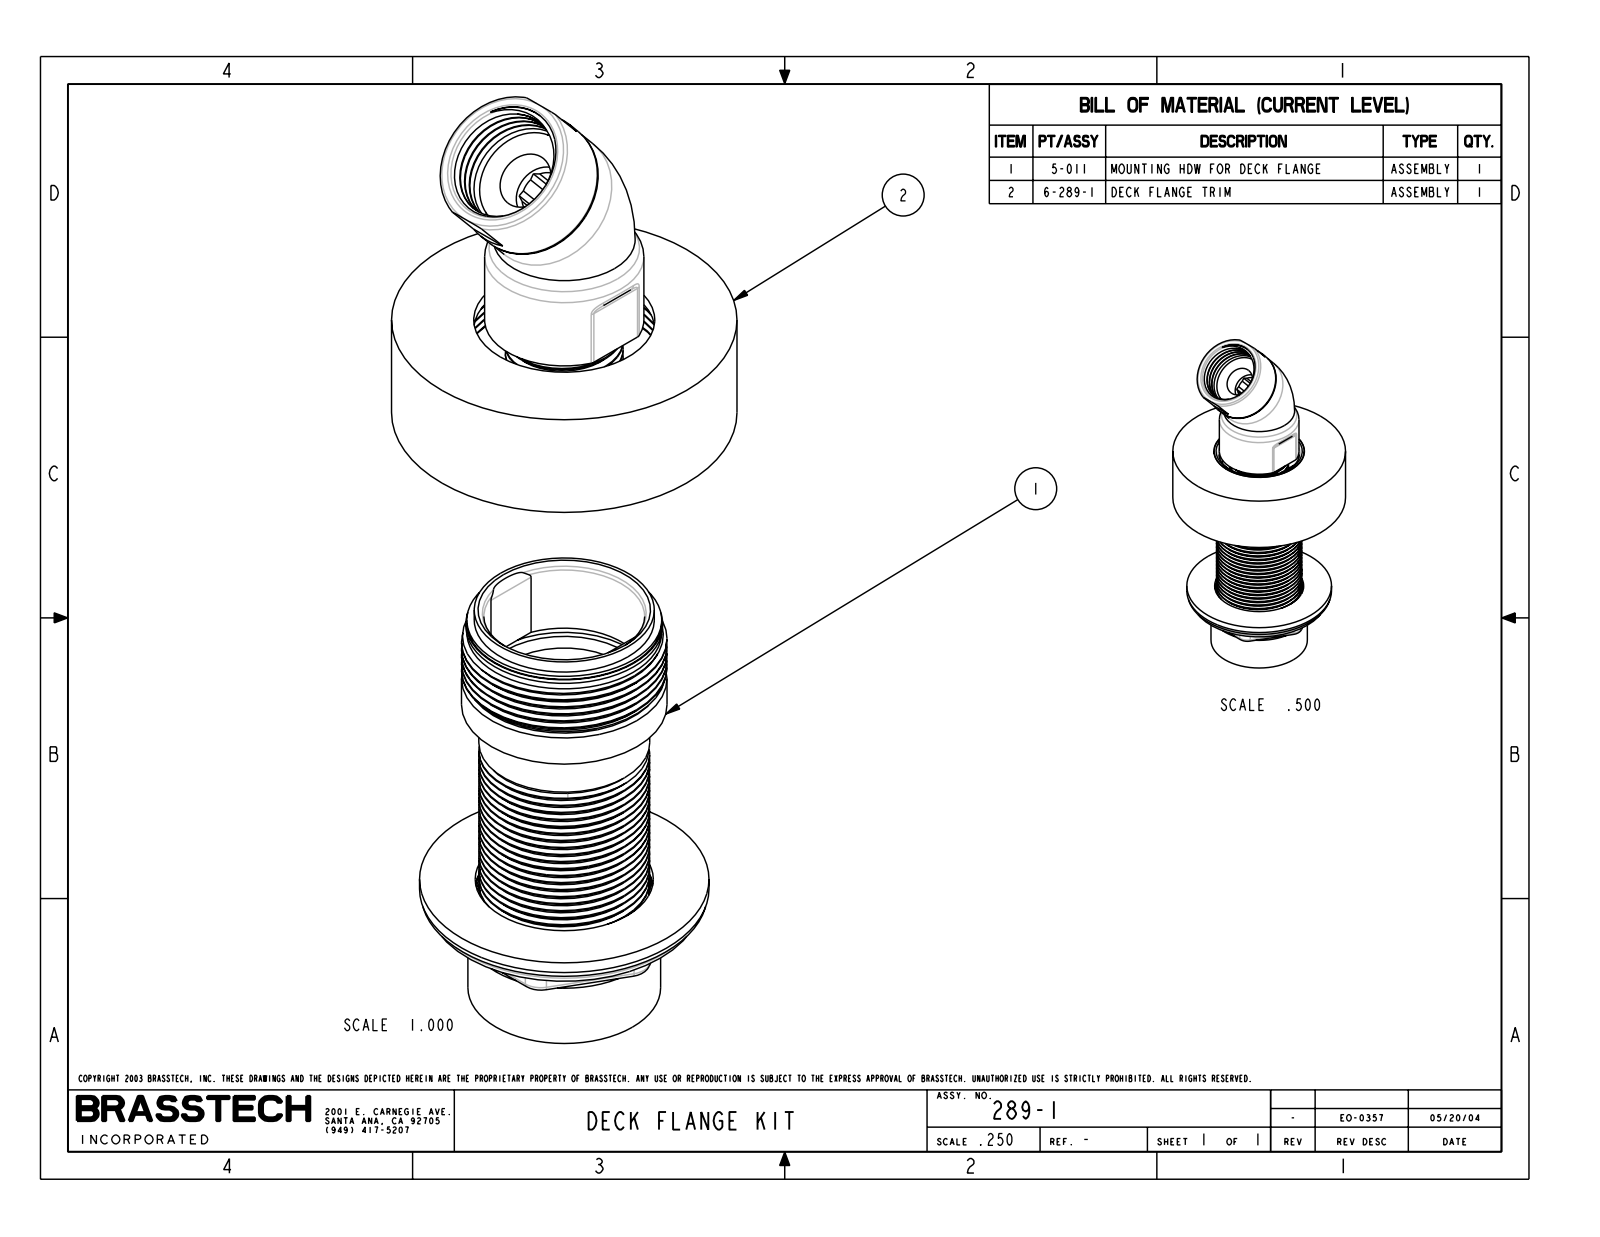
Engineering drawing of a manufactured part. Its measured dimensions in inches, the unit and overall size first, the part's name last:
Units: inches
Overall size (bounding box): 5.107 × 2.375 × 2.375
Round bosses / shafts (diameter × count): ⌀2.375 ×1, ⌀1.969 ×1, ⌀1.895 ×1, ⌀1.413 ×1, ⌀1.325 ×1, ⌀1.175 ×1, ⌀1.111 ×1, ⌀1.095 ×1
Partial cylindrical surfaces — rounded edges, fillets, slot ends (radius × count): R0.04 ×6, R0.05 ×6, R0.15 ×6
Main face-to-face distances: 0.78, 0.039, 1.607, 2.387, 1.568, 2.348, 0.092, 0.131, 1.699, 2.479
Bodies: 0 solids, 186 faces (26 planar, 110 cylindrical, 50 other)
Part name (STEP PRODUCT): 289-1_WEB
STEP written by: PRO/ENGINEER BY PARAMETRIC TECHNOLOGY CORPORATION, 2009300 (CONFIG_CONTROL_DESIGN)
